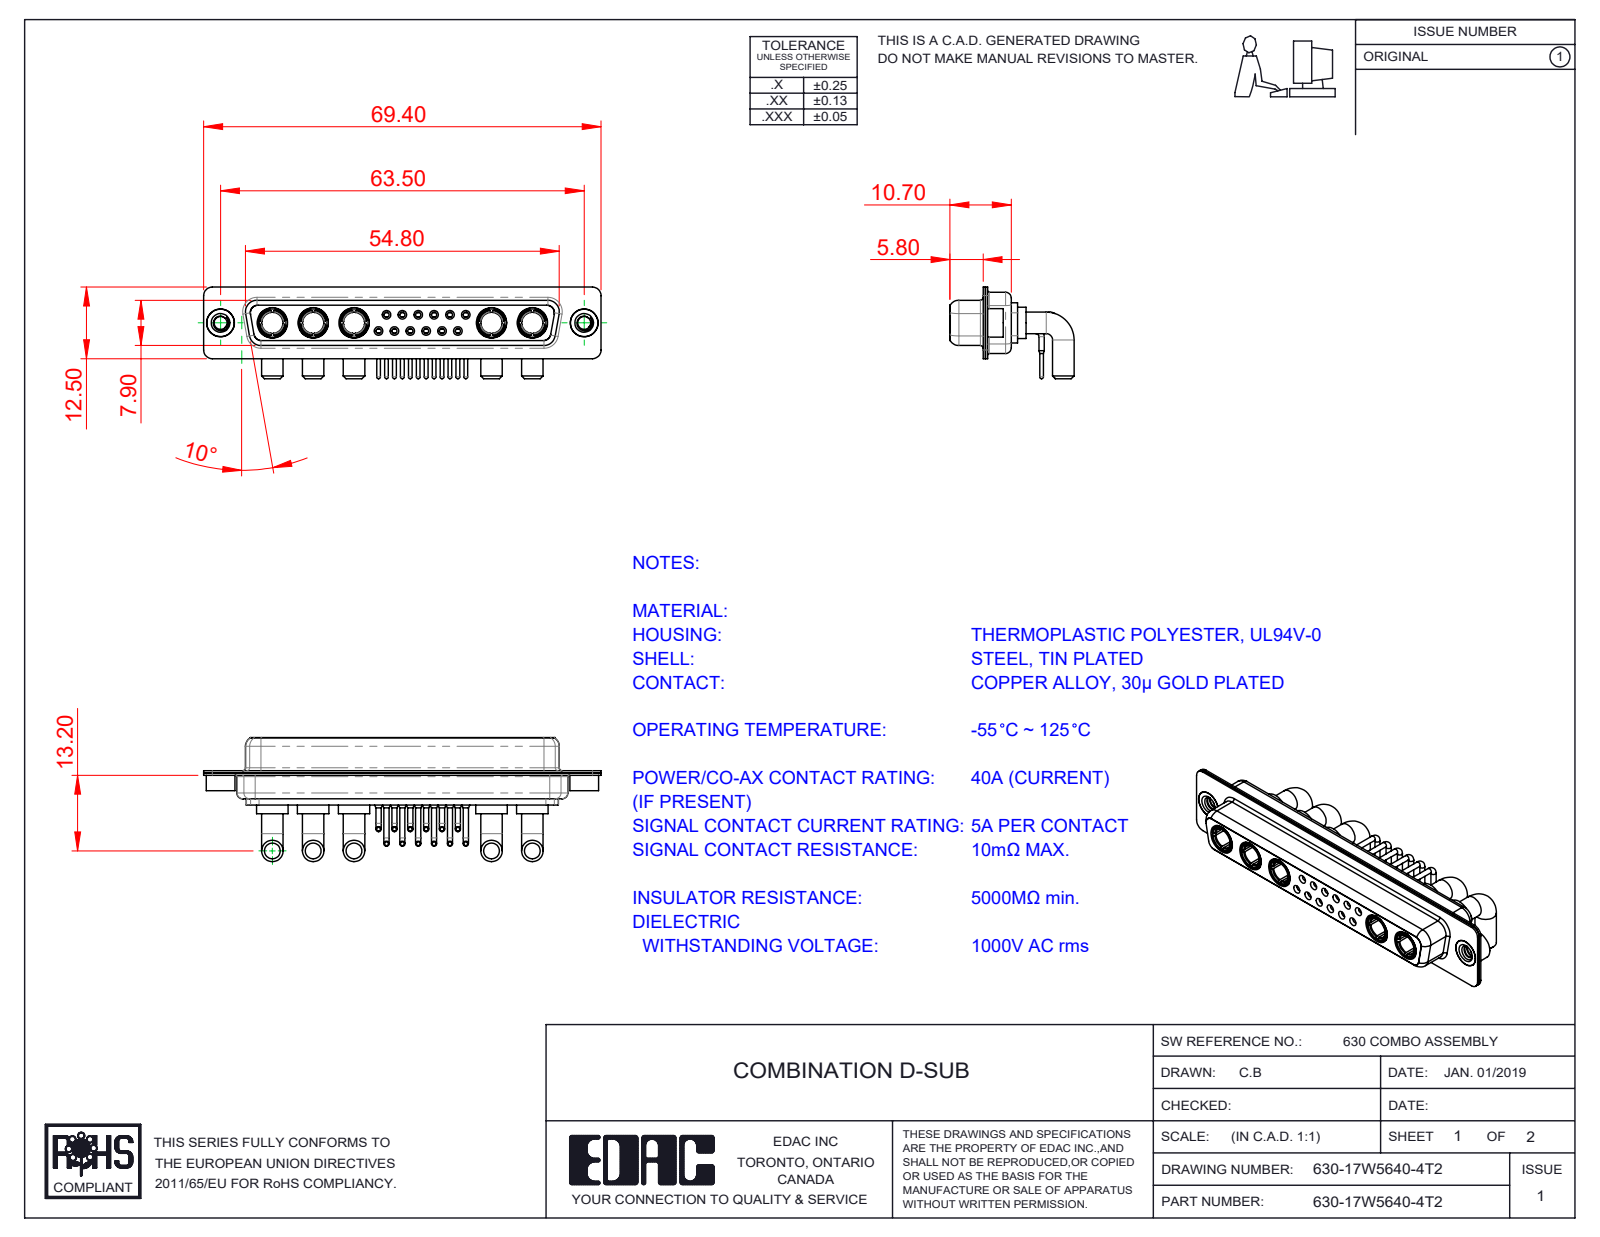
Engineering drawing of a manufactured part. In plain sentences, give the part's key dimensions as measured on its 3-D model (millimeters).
The part is named "630Combo Contact Row 1; 630Combo Housing_17W5; 630Combo Shell Front_37 Contacts; 630Combo Shell Rear_37 Contacts (+4 more)". Its 3-D file was written by "SolidWorks 2020 (CONFIG_CONTROL_DESIGN)". It is 27 solids with 1305 faces: 392 planar, 538 cylindrical and 375 other. Overall it measures 69.4 by 21.68 by 16 millimeters. Its volume is 6 039 cubic millimeters and its surface area 12 603 square millimeters. Round holes: 12 of diameter 0.9, 12 of diameter 1.1, 12 of diameter 1.5, 12 of diameter 2, 7 of diameter 4.85, 6 of diameter 1.6, 6 of diameter 1.7, 5 of diameter 3.7, 5 of diameter 5.3, 2 of diameter 2.26, 2 of diameter 4, 2 of diameter 4.05. Round bosses or shafts: 13 of diameter 0.9, 12 of diameter 0.65, 10 of diameter 3.75, 7 of diameter 1.6, 5 of diameter 5.5, 5 of diameter 5.2, 5 of diameter 4.96, 5 of diameter 4.75. Partial cylindrical surfaces (rounded edges, fillets, slot ends): 16 of radius 1.5, 12 of radius 2, 8 of radius 1.35, 8 of radius 1.6, 5 of radius 2.1, 4 of radius 0.25, 4 of radius 0.5, 4 of radius 0.6. The main face-to-face distances are 0.4, 1.4, 0.45, 8.45, 8.9, 1.8, 6.2, 7.05, 1.85, 7.5. The hole center spacings are 3.16, 2.77, 5.04, 5.54, 5.03, 7.49, 8.31, 10.11.
